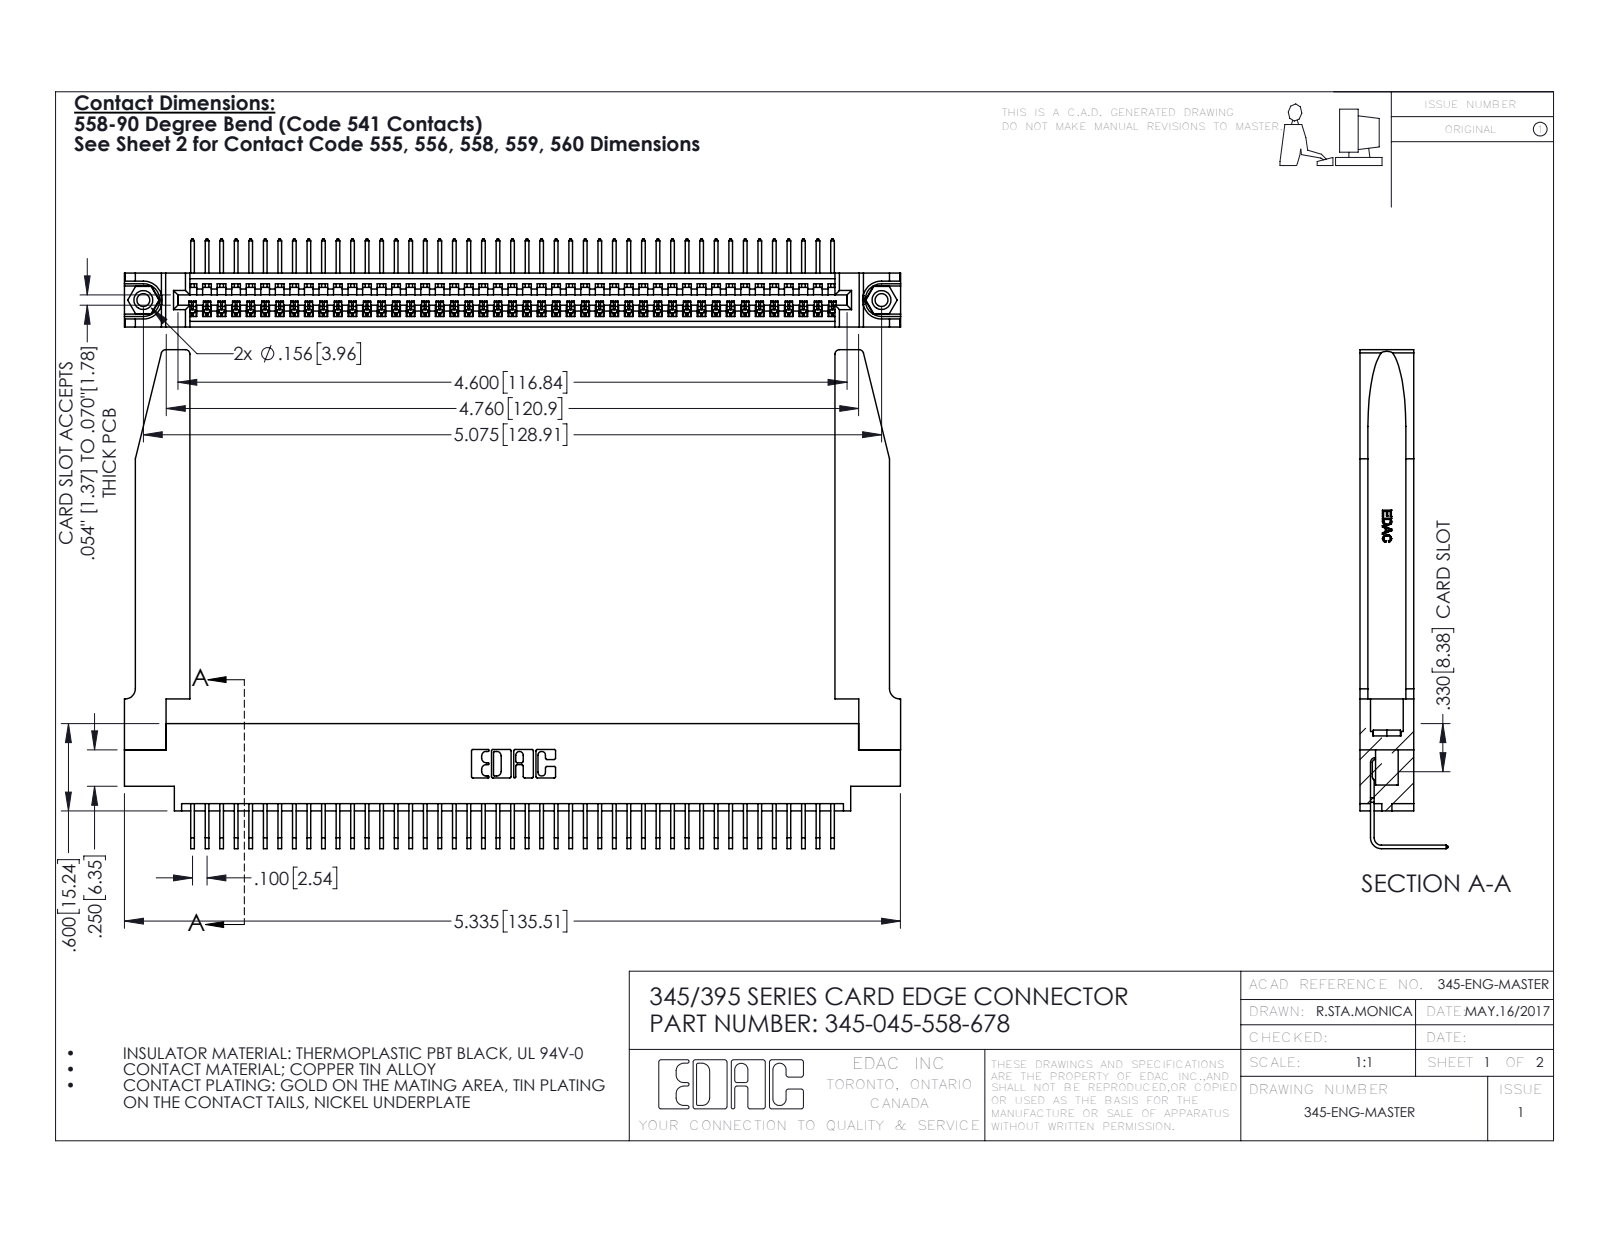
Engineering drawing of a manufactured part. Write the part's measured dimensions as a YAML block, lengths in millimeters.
part_name: "345-045-558-678; 345 Part_0.170 Offset - 0.156 Dia-TH; 345-292-001_558 Tail - 2; 345-250-001_345-250-001-102 (+1 more)"
step_written_by: "SolidWorks 2016 (CONFIG_CONTROL_DESIGN)"
units: millimeters
bodies: {solids: 50, faces: 3064, planar: 2116, cylindrical: 896, other: 52}
overall_size: [135.5, 87.1, 15.4]
volume: 20700
surface_area: 25080
round_holes:
  - {diameter: 2.3, count: 2}
  - {diameter: 3.2, count: 2}
  - {diameter: 4, count: 2}
  - {diameter: 1.6, count: 1}
round_bosses_or_shafts:
  - {diameter: 3.9, count: 2}
partial_cylinders:
  - {radius: 0.2, count: 90}
  - {radius: 0.3, count: 22}
  - {radius: 0.8, count: 8}
  - {radius: 0.2, count: 6}
  - {radius: 0.8, count: 6}
  - {radius: 0.7, count: 3}
  - {radius: 0.8, count: 2}
  - {radius: 1, count: 2}
face_to_face_distances: [9.4, 1.8, 7.6, 2.5, 6.9, 0.6, 5.1, 5.7, 3.8, 3.8]
hole_center_spacings: [6.9, 122.9, 128.9]
